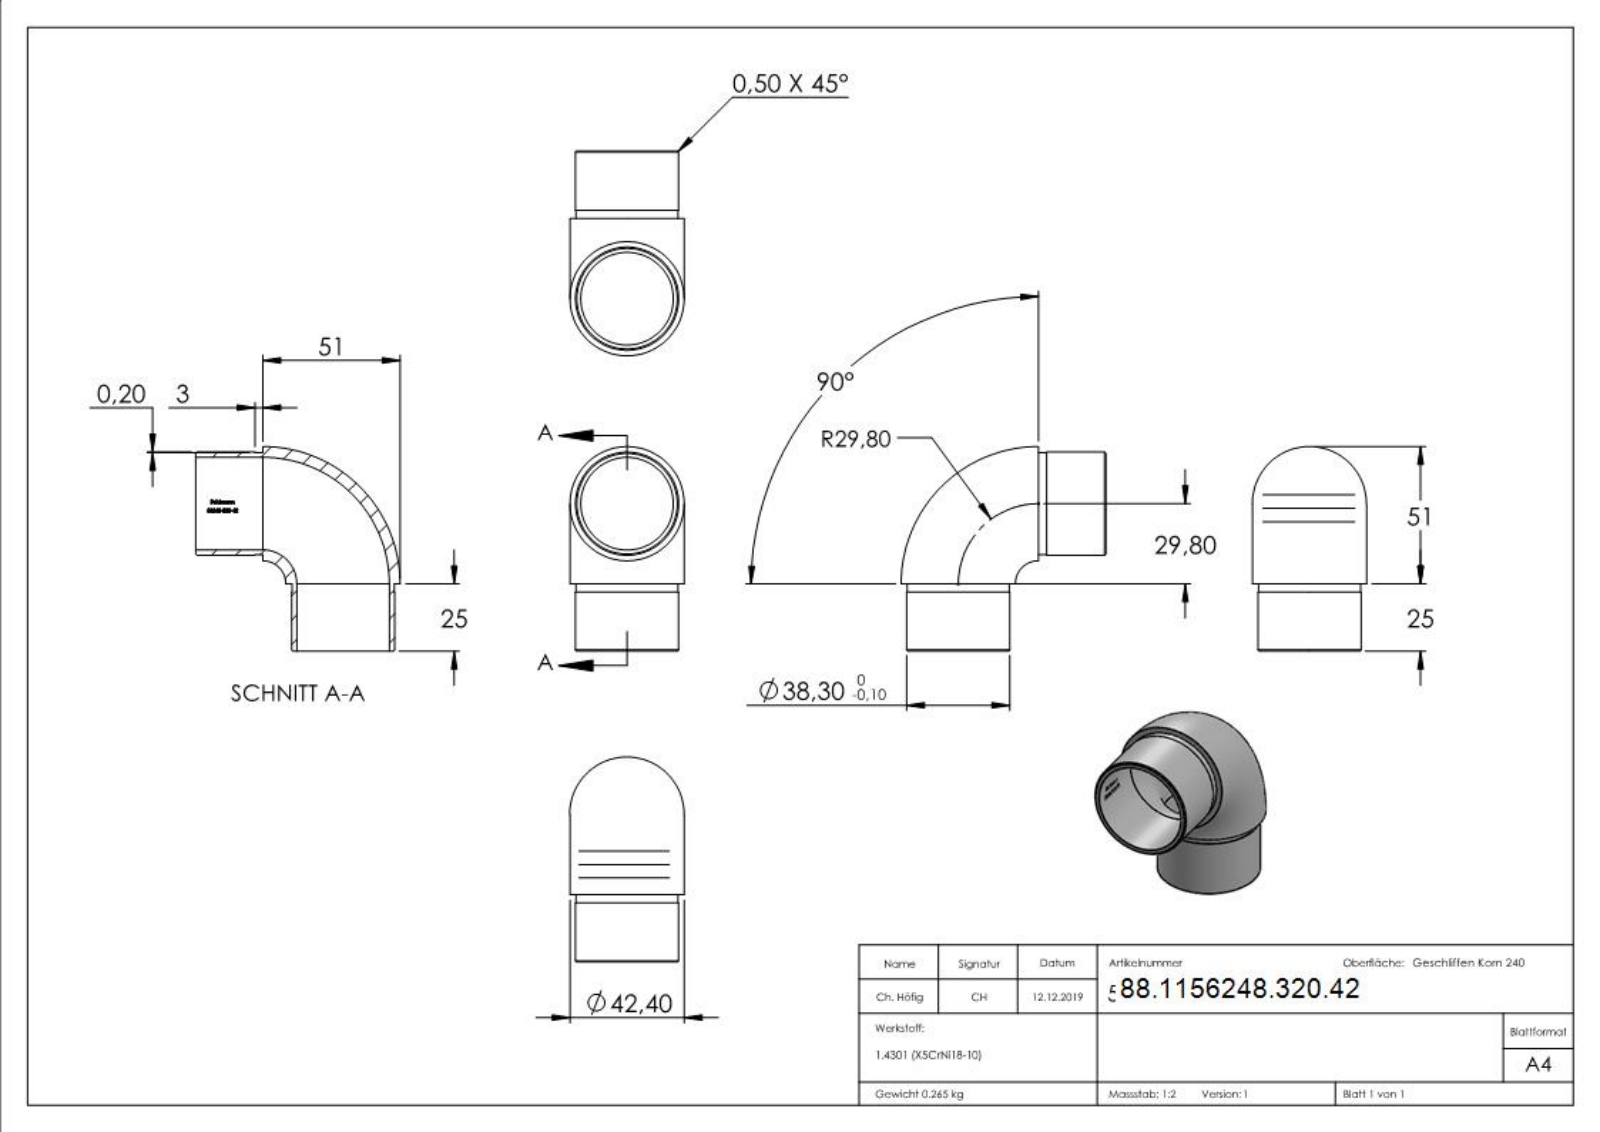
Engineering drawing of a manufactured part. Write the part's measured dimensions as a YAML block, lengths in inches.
part_name: "56248-320-42"
step_written_by: "SolidWorks 2015 (CONFIG_CONTROL_DESIGN)"
units: inches
bodies: {solids: 1, faces: 286, planar: 124, cylindrical: 35, other: 127}
overall_size: [2.992, 2.992, 1.669]
volume: 2.047
surface_area: 36.82
round_holes:
  - {diameter: 1.354, count: 2}
round_bosses_or_shafts:
  - {diameter: 1.508, count: 2}
  - {diameter: 1.492, count: 2}
partial_cylinders:
  - {radius: 0.697, count: 1}
face_to_face_distances: [0.984, 0.866, 0.118, 0.017, 2.031, 1.165, 1.047, 0.015, 0.117, 0.144]
